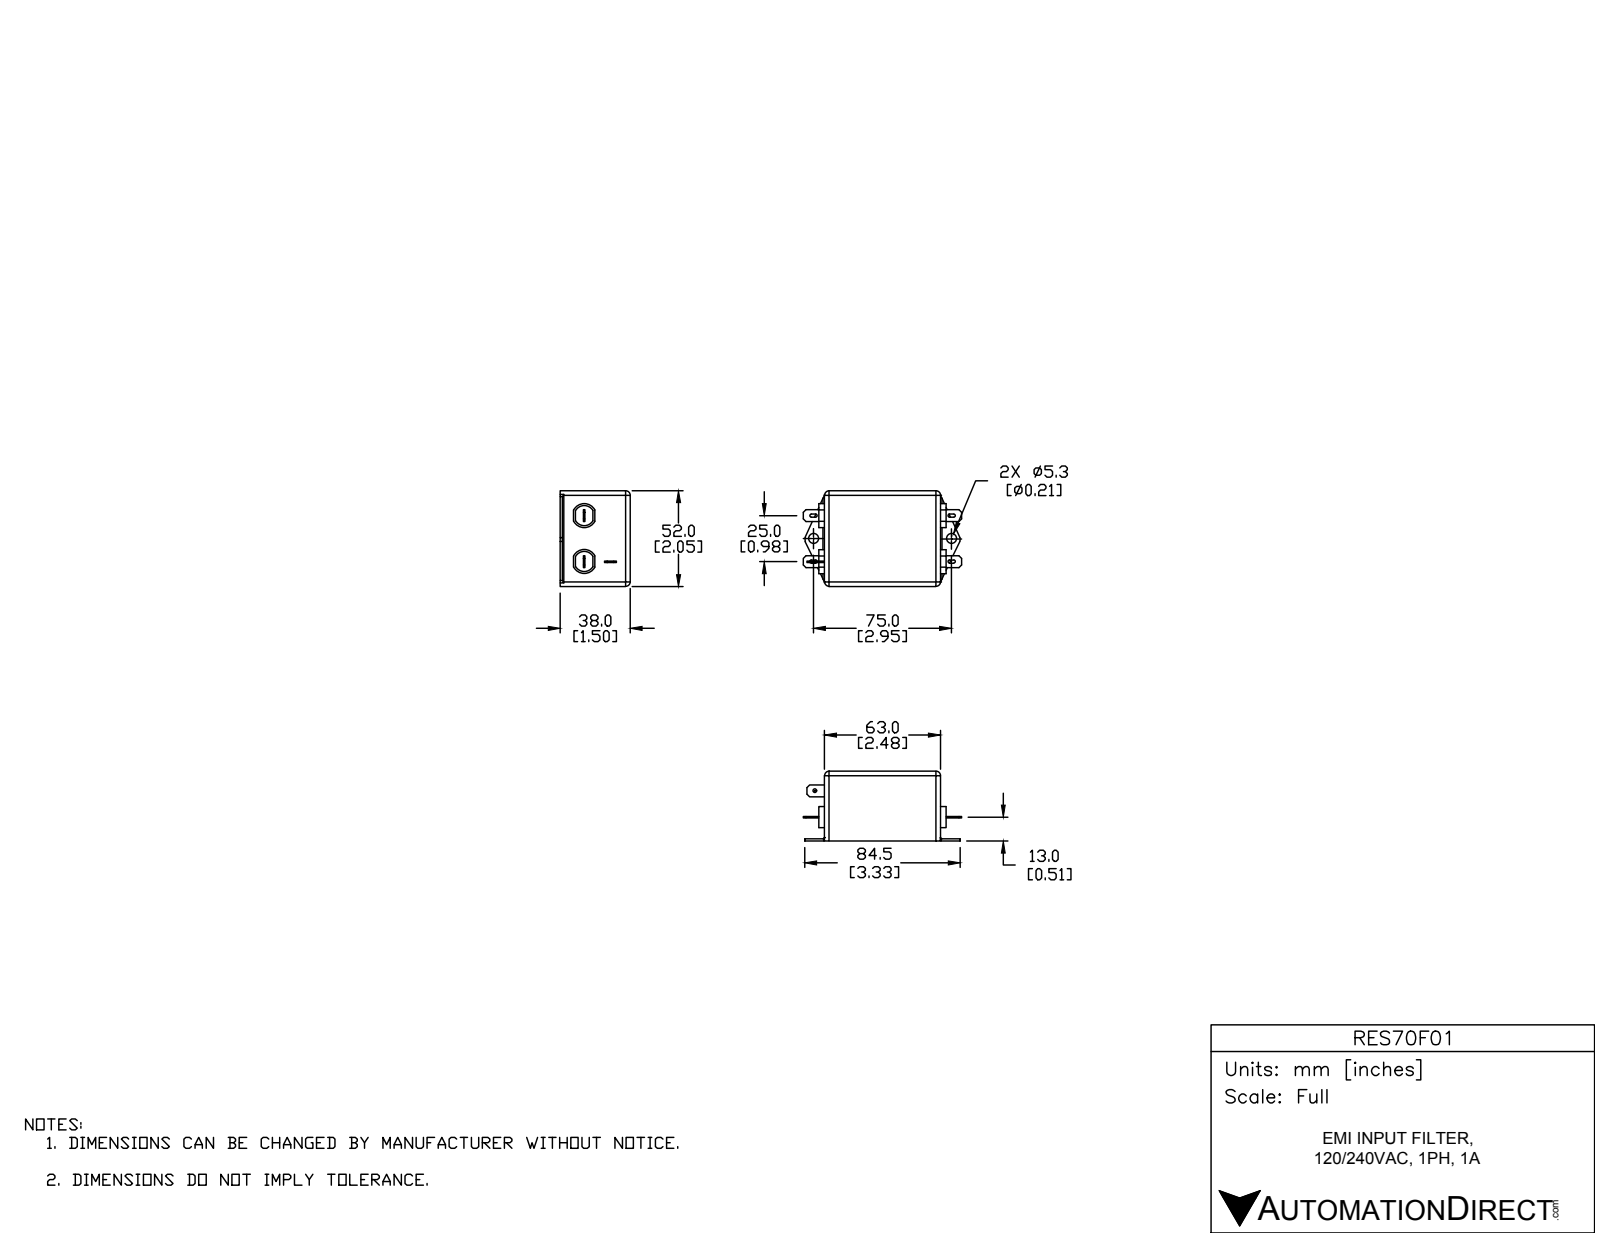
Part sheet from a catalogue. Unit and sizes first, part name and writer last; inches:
Units: inches
Overall size (bounding box): 3.386 × 2.067 × 1.161
Round holes (diameter × count): ⌀0.209 ×2, ⌀0.079 ×1
Partial cylindrical surfaces — rounded edges, fillets, slot ends (radius × count): R0.098 ×10, R0.035 ×8, R0.03 ×2, R0.217 ×2, R0.256 ×2
Main face-to-face distances: 1.161, 2.067, 2.48, 0.059, 0.047, 1.114, 2.539, 2.598, 0.031, 0.409
Hole centre spacings: 2.953
Volume: 6.036 in³ · Surface area: 23.85 in²
Bodies: 1 solid, 133 faces (79 planar, 50 cylindrical, 4 other)
Part name (STEP PRODUCT): RES70F01
STEP written by: SolidWorks 2015 (AUTOMOTIVE_DESIGN)
